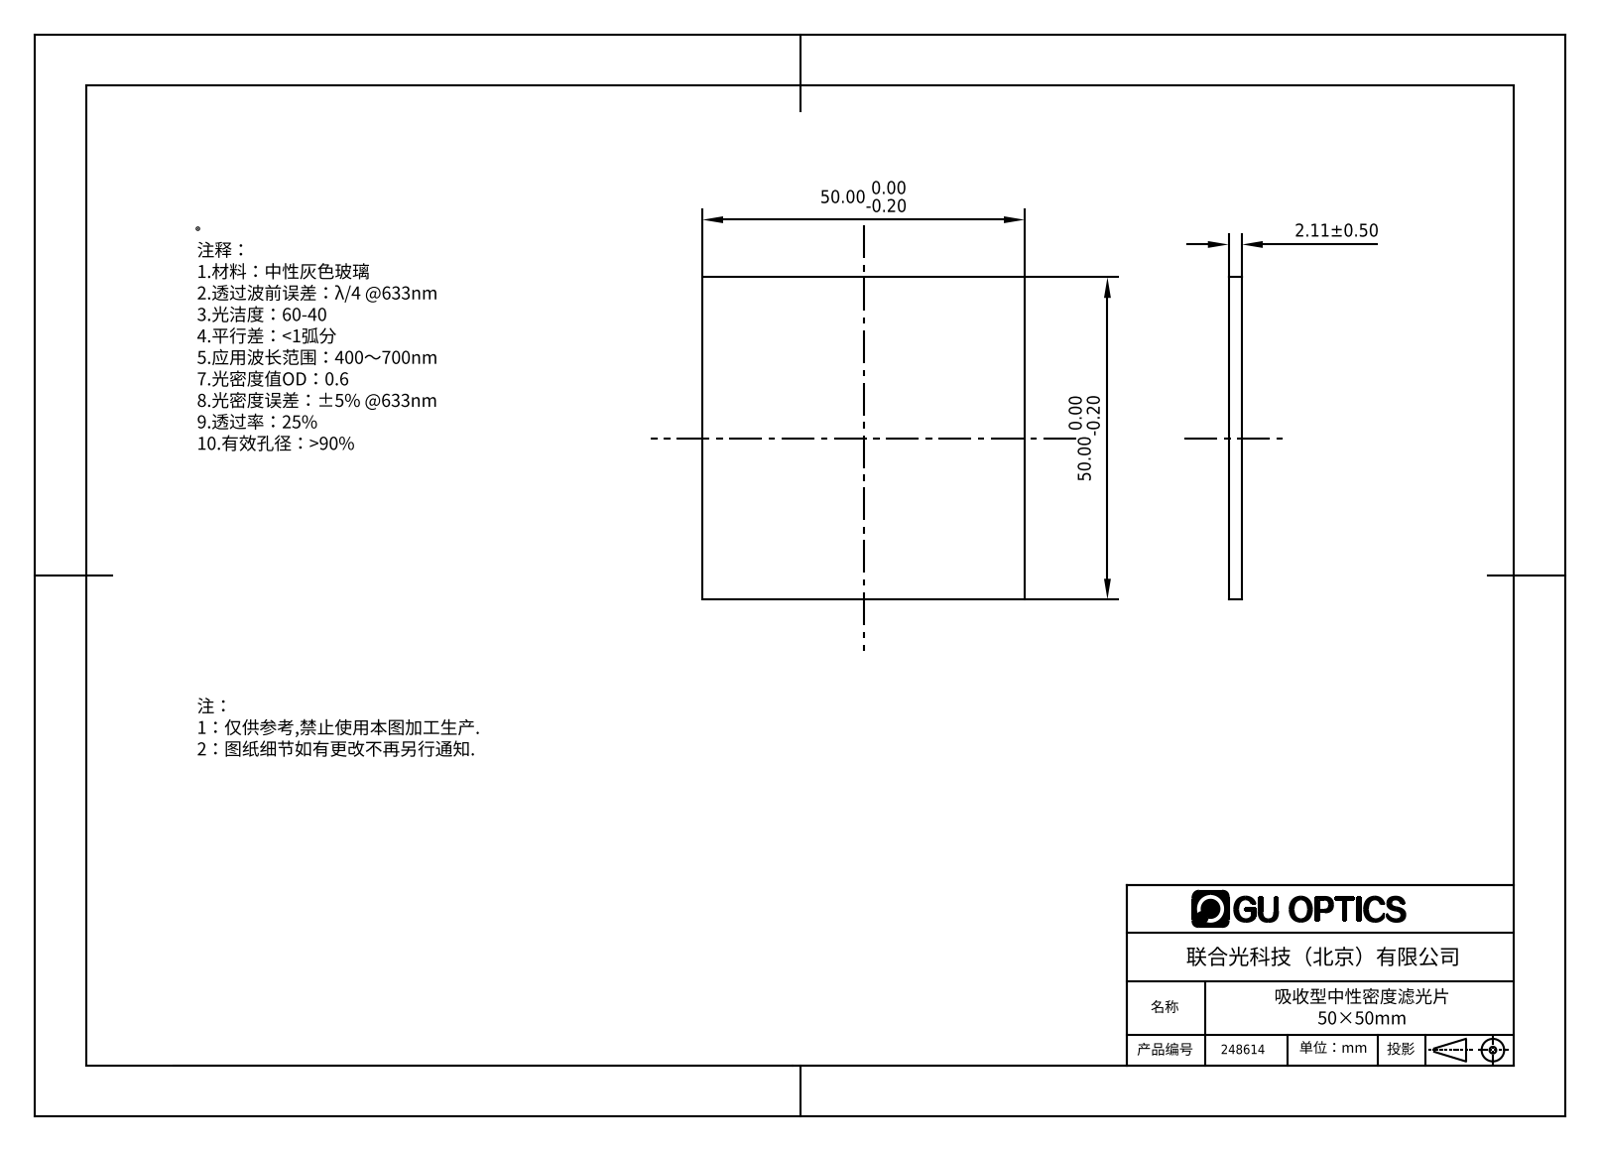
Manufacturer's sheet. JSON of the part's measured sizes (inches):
{"part_name": "248614", "step_written_by": "SolidWorks 2016 (AUTOMOTIVE_DESIGN)", "units": "inches", "bodies": {"solids": 1, "faces": 6, "planar": 6, "cylindrical": 0, "other": 0}, "overall_size": [1.969, 1.969, 0.083], "volume_in3": 0.322, "surface_area_in2": 8.404, "face_to_face_distances": [0.083, 1.969]}
